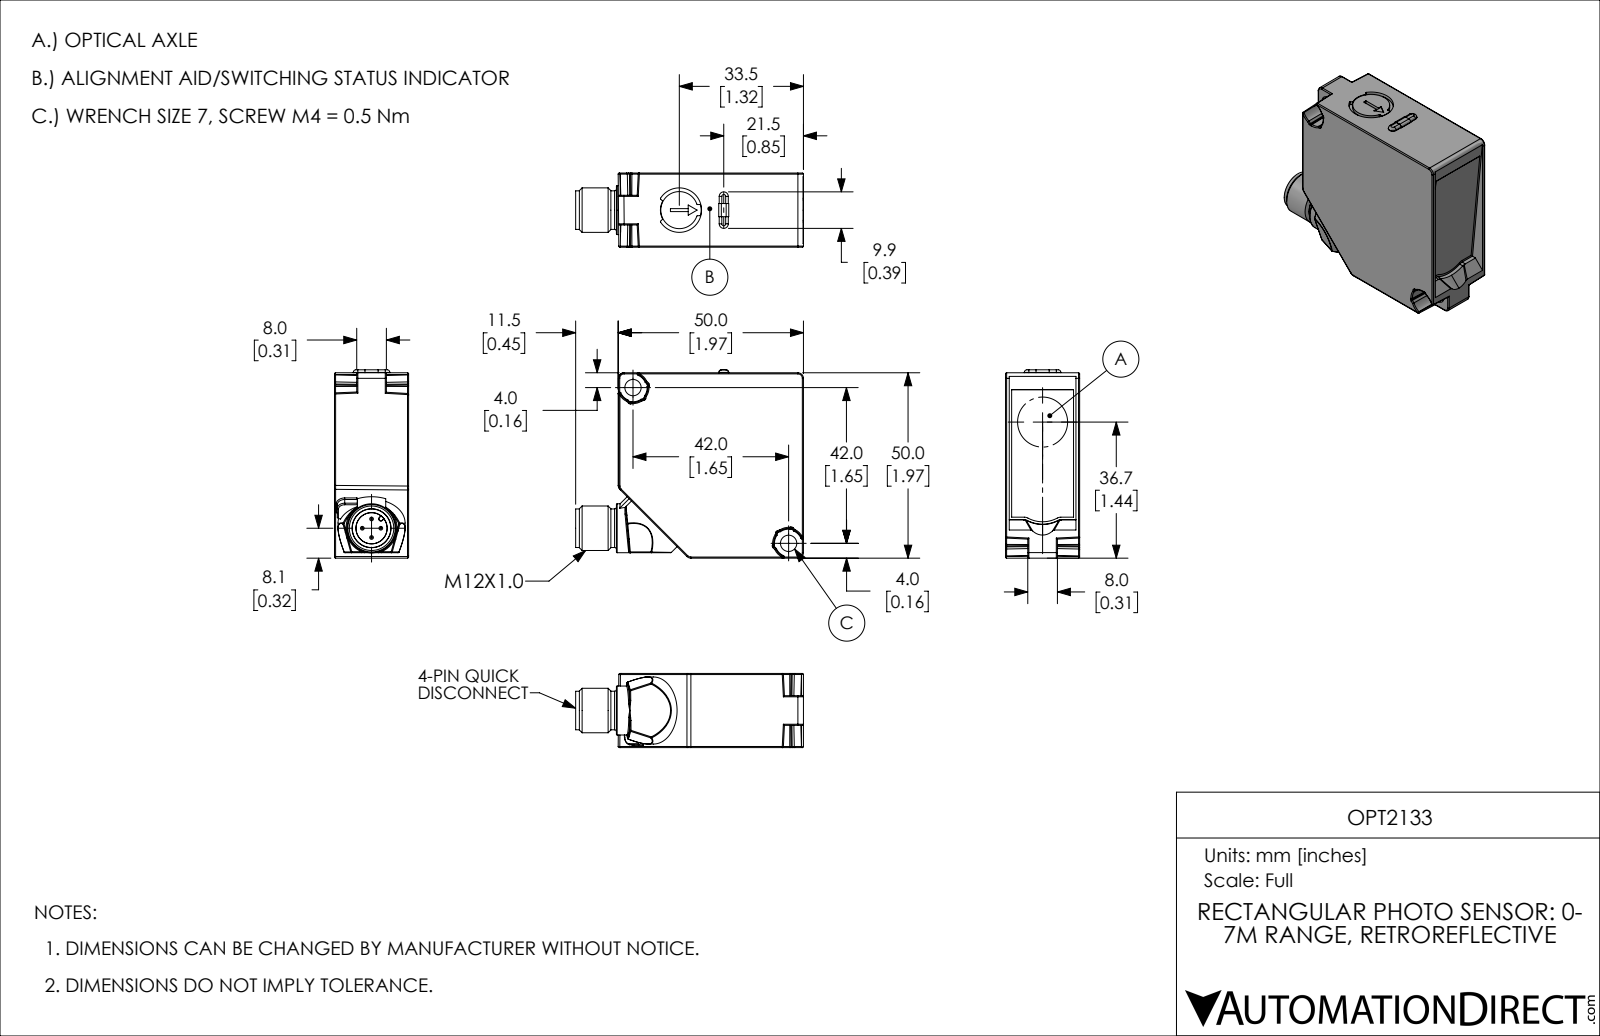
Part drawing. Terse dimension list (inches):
name: OPT2133
written by: SolidWorks 2019 (AUTOMOTIVE_DESIGN)
unit: in
bodies: 2 solids, 342 faces (110 planar, 119 cylindrical, 113 other)
size: 2.42 × 2 × 0.787
volume: 2.816 in³; area: 16.5 in²
holes: 2× ⌀0.173, 1× ⌀0.472, 1× ⌀0.713
bosses: 4× ⌀0.039, 1× ⌀0.52, 1× ⌀0.472, 1× ⌀0.409, 1× ⌀0.394
rounds: 63× R0.012, 8× R0.008, 5× R0.059, 5× R0.079, 4× R0.028, 2× R0.048, 1× R0.201, 1× R0.232
face distances: 0.787, 1.969, 0.039, 0.748, 0.236, 0.551, 0.197, 0.512, 0.058, 1.911
hole spacings: 2.339
